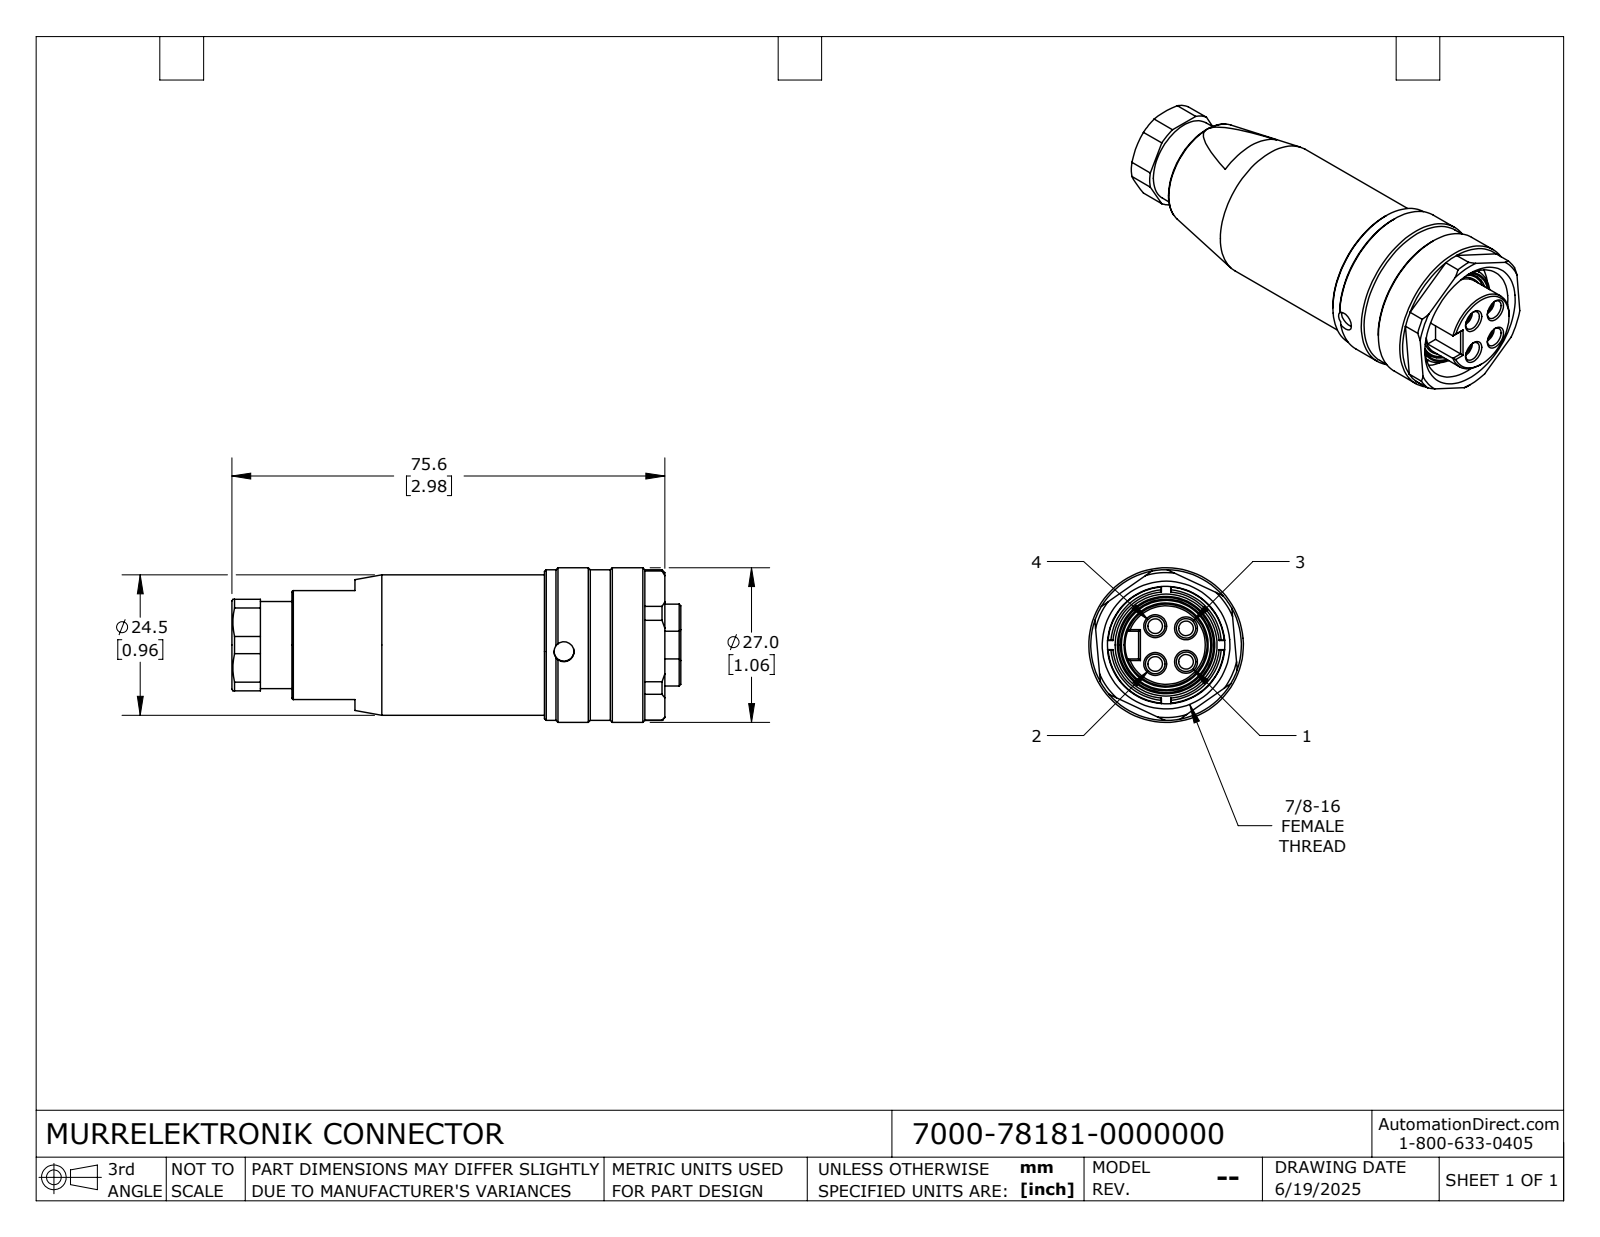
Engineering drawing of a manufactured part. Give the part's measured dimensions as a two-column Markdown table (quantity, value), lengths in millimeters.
| quantity | value |
| --- | --- |
| part name | 7000-78181-0000000 |
| STEP written by | SolidWorks 2024 (CONFIG_CONTROL_DESIGN) |
| units | millimeters |
| bodies | 1 solid, 206 faces (72 planar, 75 cylindrical, 59 other) |
| overall size | 78.4 × 27 × 27 |
| volume | 30 692 mm³ |
| surface area | 9 260 mm² |
| round holes (diameter × count) | 2.55 × 4, 3.4 × 4, 3.5 × 1, 9.5 × 1, 20.5 × 1, 24.8 × 1 |
| round bosses / shafts (diameter × count) | 27 × 1, 26.3 × 1, 24.5 × 1, 24.2 × 1, 17.8 × 1, 17.4 × 1, 15.2 × 1, 14.3 × 1 |
| partial cylindrical surfaces (radius × count) | 0.5 × 4, 8.5 × 1, 10.6 × 1, 12.5 × 1 |
| main face-to-face distances | 24, 4.5, 5.9, 19, 5, 59.2, 65.1, 67.9, 8.7, 2.8 |
| hole center spacings | 3.81, 4.54, 5.39, 8.22, 5.84, 6.6 |
